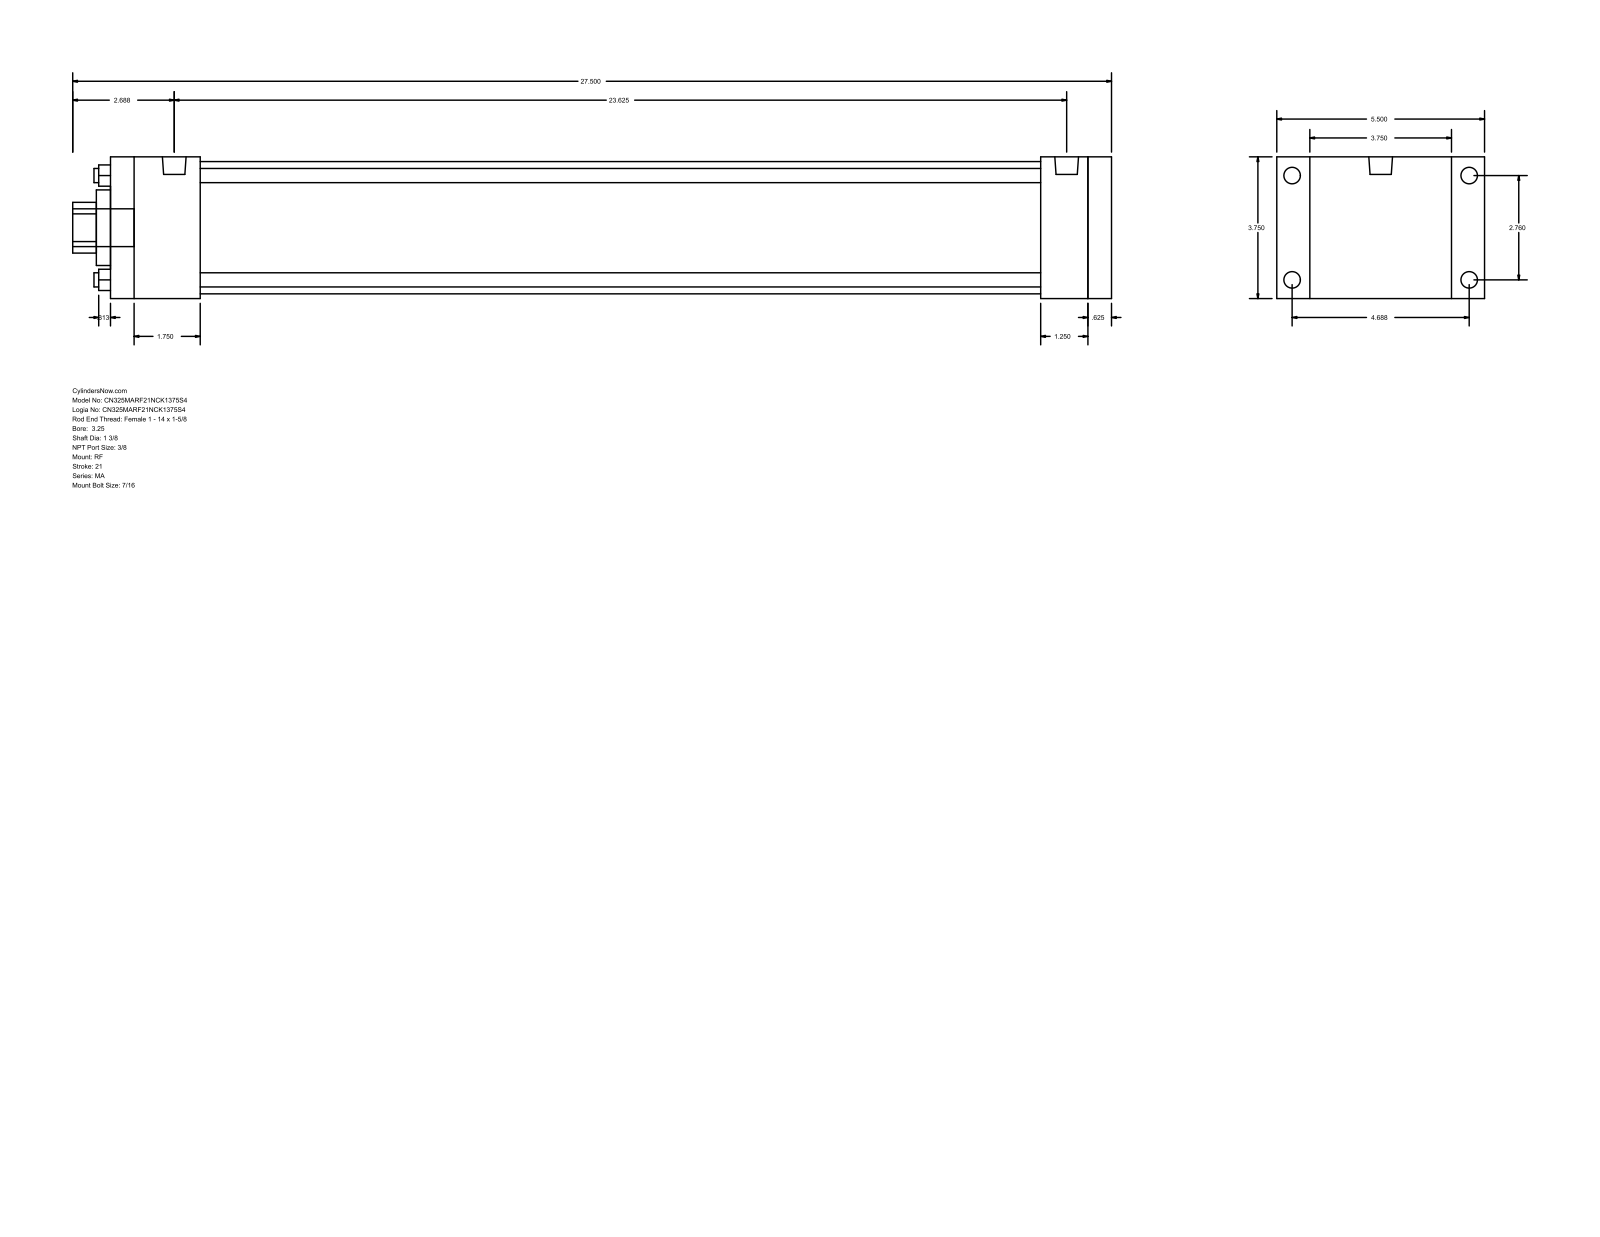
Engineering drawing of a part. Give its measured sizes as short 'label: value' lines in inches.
name: MA_RF__0325_1.375
written by: GSSL Pune (CONFIG_CONTROL_DESIGN)
unit: in
bodies: 0 solids, 92 faces (64 planar, 28 cylindrical, 0 other)
size: 27.5 × 5.5 × 3.75
holes: 4× ⌀0.375, 1× ⌀1.375, 1× ⌀2, 1× ⌀3.5
bosses: 8× ⌀0.437, 2× ⌀0.627, 1× ⌀1
rounds: 1× R0.672
face distances: 3.75, 26.5, 0.625, 25.875, 0.875, 4.625, 24.625, 1.25, 1.875, 2.375
hole spacings: 1.952, 2.76, 3.903
